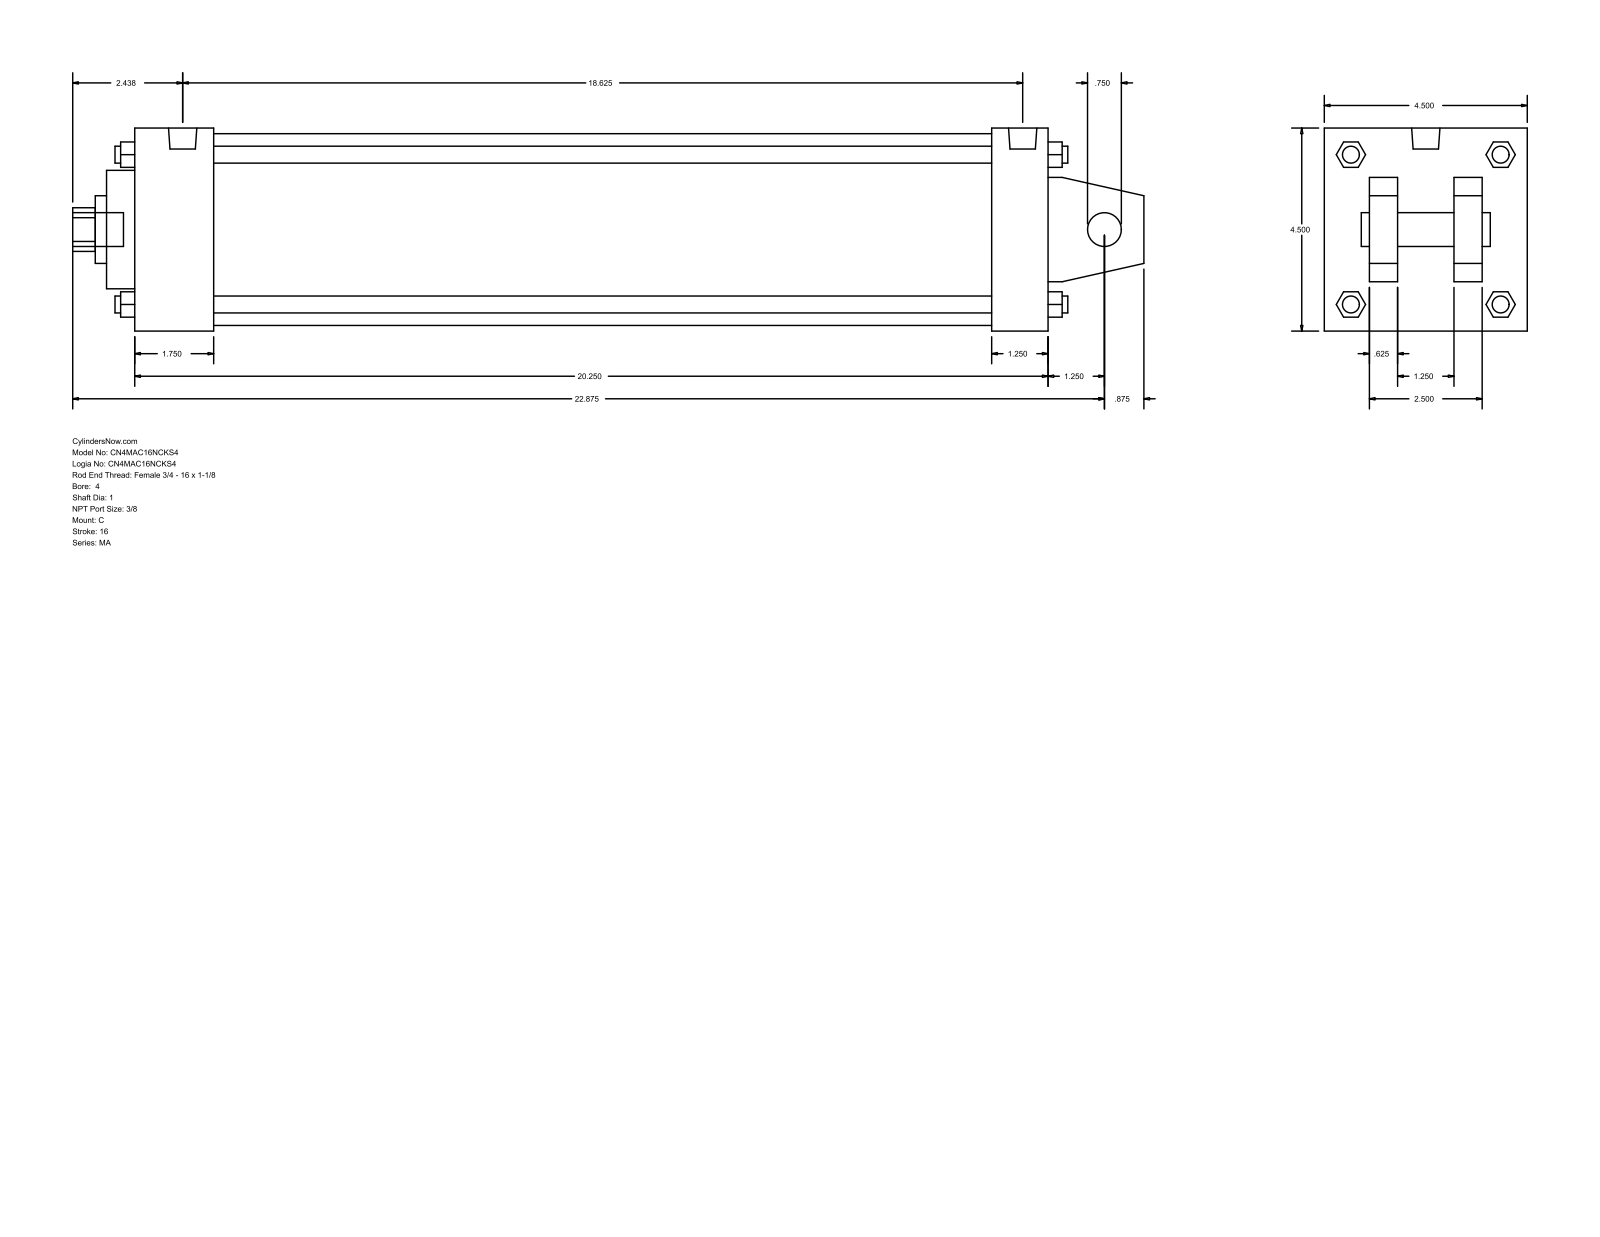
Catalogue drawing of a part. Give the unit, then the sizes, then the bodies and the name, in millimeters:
Units: millimetres
Overall size (bounding box): 603.25 × 114.3 × 114.3
Round holes (diameter × count): ⌀19.05 ×1, ⌀25.4 ×1, ⌀38.1 ×1, ⌀66.67 ×1, ⌀107.95 ×1
Round bosses / shafts (diameter × count): ⌀11.11 ×4, ⌀9.53 ×4, ⌀15.93 ×2, ⌀19.05 ×1
Partial cylindrical surfaces — rounded edges, fillets, slot ends (radius × count): R12.29 ×1
Main face-to-face distances: 114.3, 514.35, 15.87, 73.03, 41.27, 25.4, 88.9, 47.63, 482.6, 31.75
Bodies: 0 solids, 141 faces (109 planar, 32 cylindrical, 0 other)
Part name (STEP PRODUCT): MA_C__0400_1
STEP written by: GSSL Pune (CONFIG_CONTROL_DESIGN)
